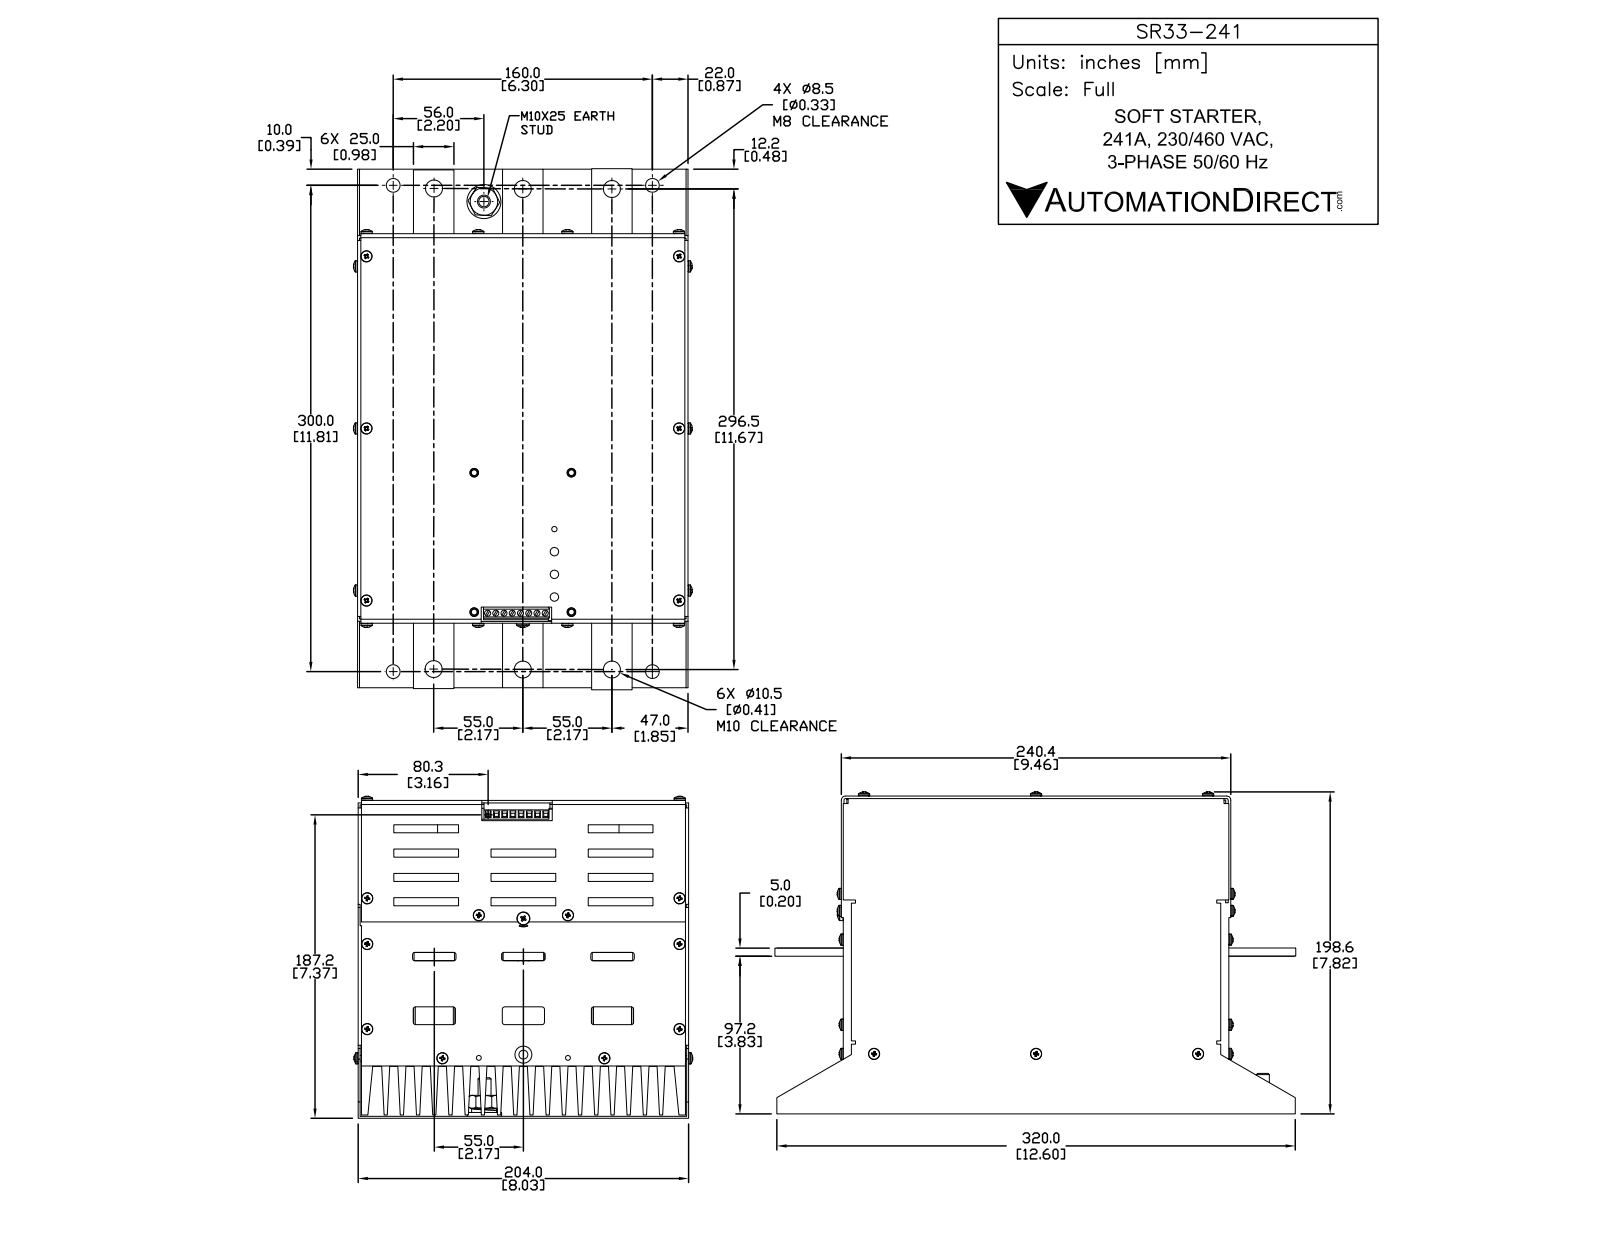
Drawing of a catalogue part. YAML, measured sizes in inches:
part_name: "SR33-241"
step_written_by: "SolidWorks 2013 (AUTOMOTIVE_DESIGN)"
units: inches
bodies: {solids: 2, faces: 1114, planar: 755, cylindrical: 153, other: 206}
overall_size: [12.709, 7.992, 7.839]
volume: 484
surface_area: 1549
round_holes:
  - {diameter: 0.15, count: 8}
  - {diameter: 0.335, count: 4}
round_bosses_or_shafts:
  - {diameter: 0.272, count: 14}
  - {diameter: 0.63, count: 7}
  - {diameter: 0.315, count: 7}
partial_cylinders:
  - {radius: 0.079, count: 14}
  - {radius: 0.039, count: 8}
face_to_face_distances: [0.393, 0.787, 1.18, 1.573, 1.967, 2.36, 0.591, 2.753, 3.146, 3.54]
hole_center_spacings: [0.194, 0.387, 0.581, 0.775, 0.969, 1.162, 6.299, 11.811]
